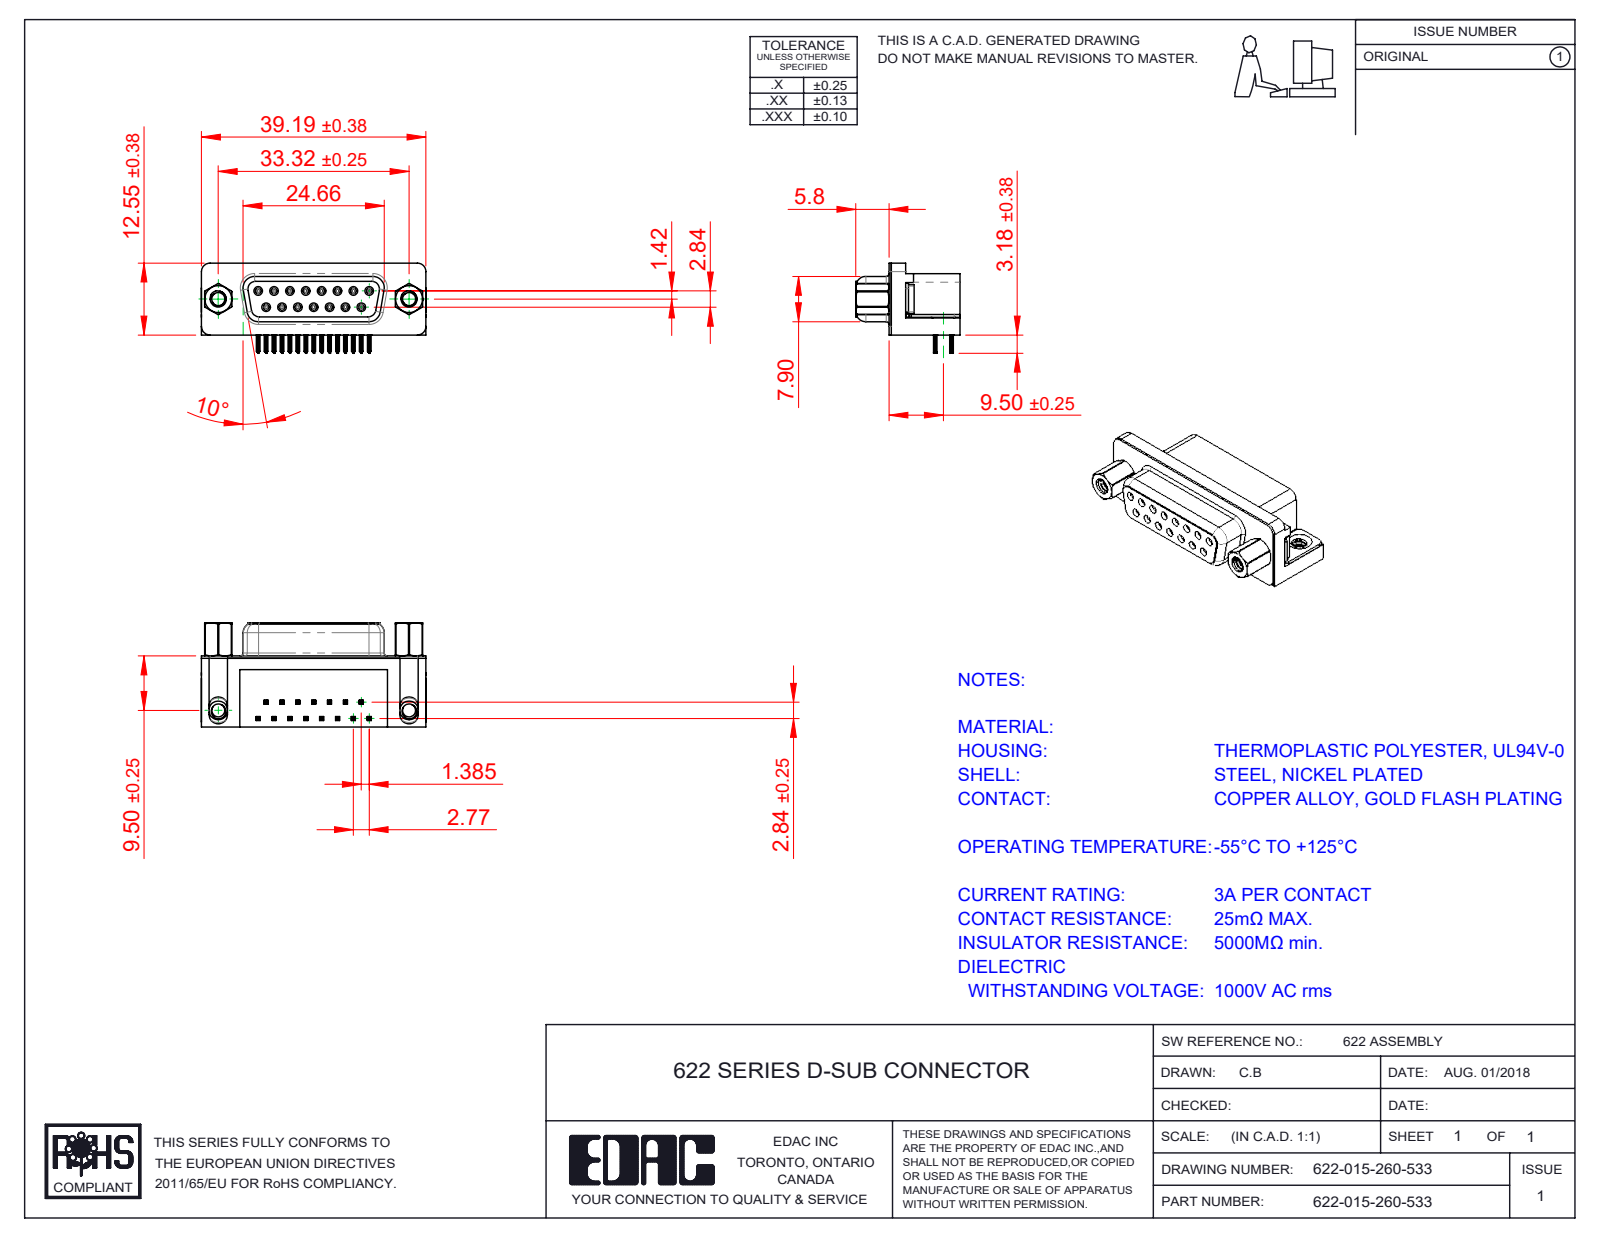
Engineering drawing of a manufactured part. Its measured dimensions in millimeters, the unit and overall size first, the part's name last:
Units: millimetres
Overall size (bounding box): 39.22 × 18.2 × 16.25
Round holes (diameter × count): ⌀0.8 ×15, ⌀0.9 ×15, ⌀2.26 ×2, ⌀2.29 ×2, ⌀4 ×2, ⌀4.8 ×2, ⌀5 ×2
Round bosses / shafts (diameter × count): ⌀1.2 ×15, ⌀4.9 ×2, ⌀4.75 ×2, ⌀3.9 ×2, ⌀2.79 ×2
Partial cylindrical surfaces — rounded edges, fillets, slot ends (radius × count): R0.1 ×120, R0.15 ×60, R0.35 ×30, R1 ×18, R0.34 ×15, R0.5 ×10, R0.25 ×8, R1.35 ×8
Main face-to-face distances: 0.4, 12, 6.2, 12.4, 10.35, 2.9, 0.85, 6.65, 0.35, 5.8
Hole centre spacings: 3.16, 2.77, 5.54, 8.31, 11.08, 5.03, 5.04, 7.48
Volume: 5 389 mm³ · Surface area: 7 174 mm²
Bodies: 23 solids, 2587 faces (1128 planar, 677 cylindrical, 782 other)
Part name (STEP PRODUCT): 622 Contact Top; 622 2 Prong Board Lock; 622 4-40 Threaded Rivet; 622 Shell_15 Socket (+4 more)
STEP written by: SolidWorks 2016 (CONFIG_CONTROL_DESIGN)
